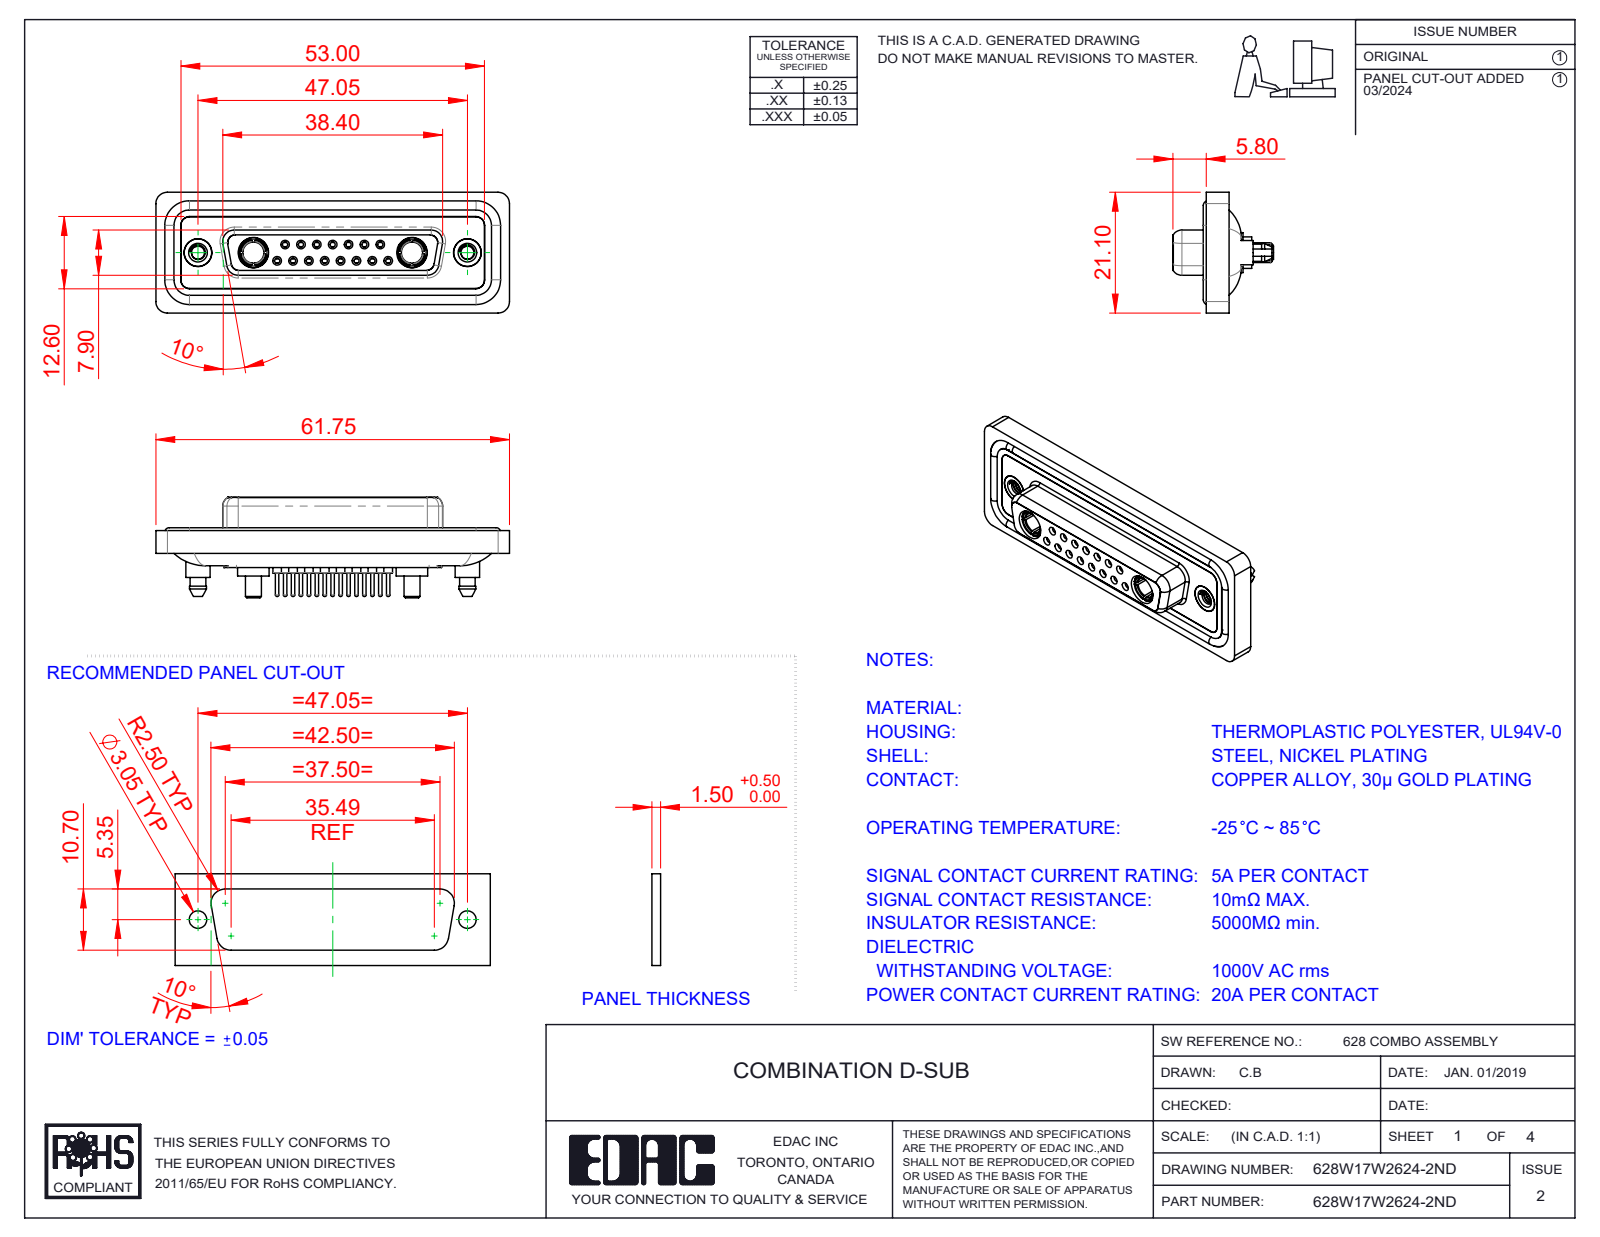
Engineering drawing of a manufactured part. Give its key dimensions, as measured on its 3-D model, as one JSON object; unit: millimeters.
{"part_name": "628Combo Shell Rear_25 Contacts; 628Combo Contact Row 2_24; 628Combo Threaded Boardlock_D; Power Socket_20A S (+5 more)", "step_written_by": "SolidWorks 2023 (CONFIG_CONTROL_DESIGN)", "units": "millimeters", "bodies": {"solids": 26, "faces": 1425, "planar": 404, "cylindrical": 567, "other": 454}, "overall_size": [61.75, 21.1, 17.55], "volume_mm3": 8459, "surface_area_mm2": 14194, "round_holes": [[0.9, 15], [1.1, 15], [1.5, 15], [2, 15], [1.6, 8], [1.7, 7], [4.85, 4], [2.26, 2], [3.7, 2], [4, 2], [4.05, 2], [5, 2]], "round_bosses_or_shafts": [[2.2, 15], [0.6, 15], [1.6, 11], [5.5, 2], [5.4, 2], [5.2, 2], [4.96, 2], [4.95, 2]], "partial_cylinders_radius": [[1.5, 24], [2, 18], [1.6, 10], [1.35, 8], [0.25, 4], [0.5, 4], [0.6, 4], [0.65, 4]], "face_to_face_distances": [0.4, 1.8, 7.45, 5.65, 6.6, 0.5, 7.05, 1.6, 2.9, 1.1], "hole_center_spacings": [3.16, 2.77, 8.31, 5.54, 5.03, 5.04, 7.49, 11.08]}
